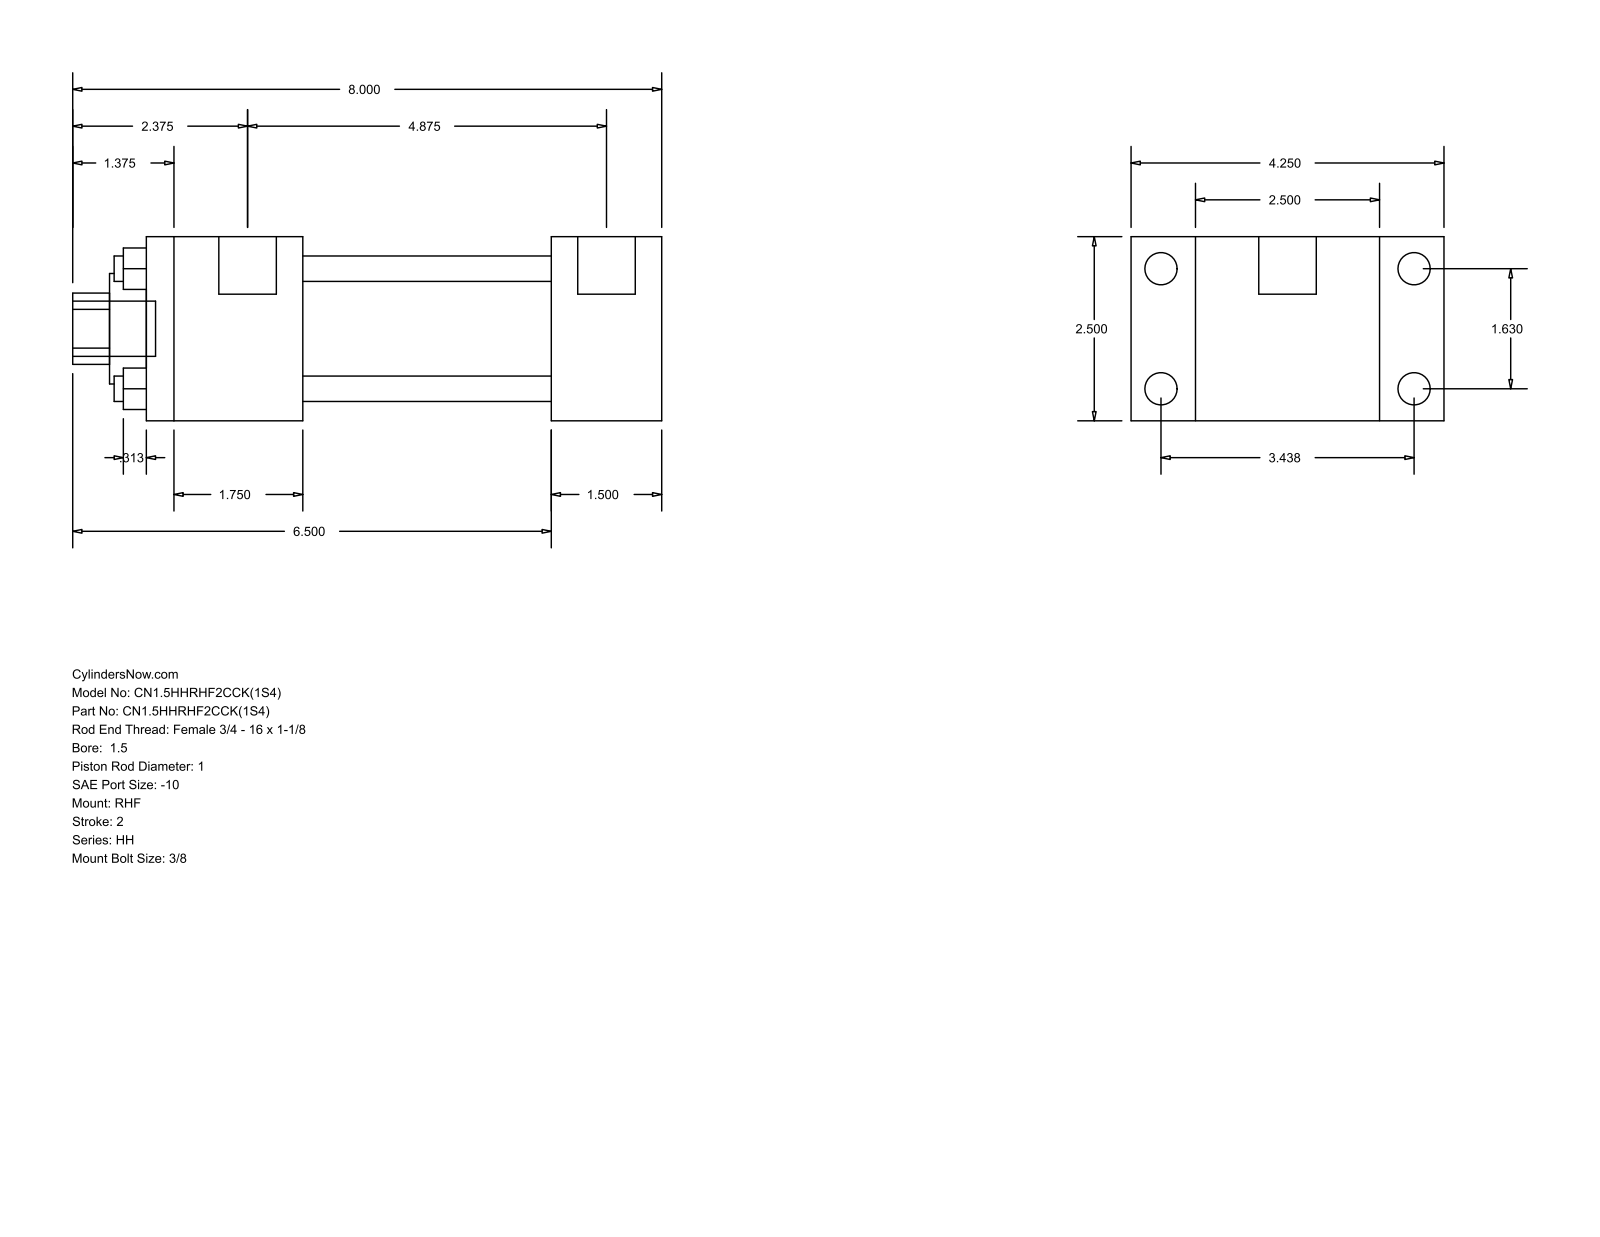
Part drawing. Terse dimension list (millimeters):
name: HH_RHF__0150_1
written by: GSSL Pune (CONFIG_CONTROL_DESIGN)
unit: mm
bodies: 0 solids, 88 faces (60 planar, 28 cylindrical, 0 other)
size: 203.2 × 107.95 × 63.5
holes: 4× ⌀8.76, 1× ⌀25.4, 1× ⌀38.1, 1× ⌀44.45
bosses: 4× ⌀11.13, 4× ⌀5.56, 2× ⌀19.84, 1× ⌀19.05
rounds: 1× R12.29
face distances: 63.5, 22.23, 85.73, 38.1, 107.96, 85.72, 123.82, 53.98, 139.7, 177.8
hole spacings: 29.27, 41.4, 58.55
